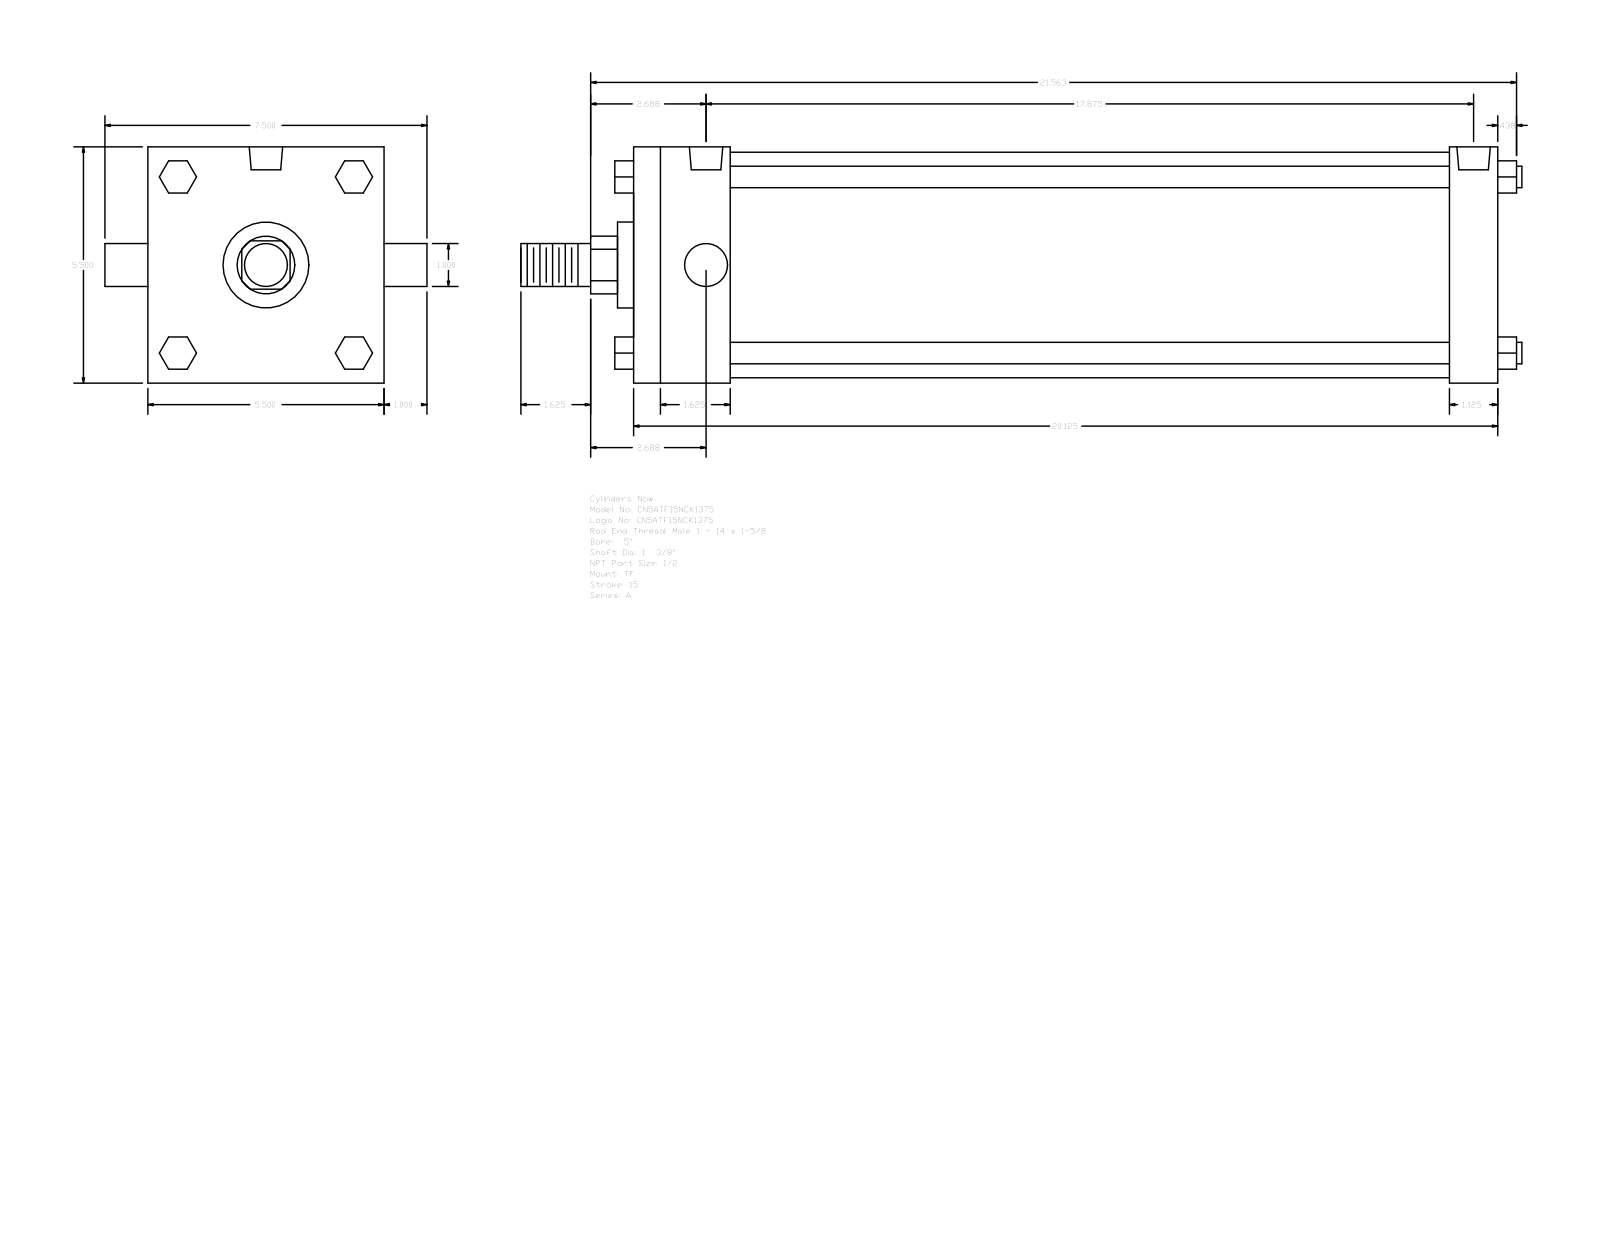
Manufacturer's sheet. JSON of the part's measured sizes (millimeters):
{"part_name": "A_TF__0500_1.375", "step_written_by": "GSSL Pune (CONFIG_CONTROL_DESIGN)", "units": "millimeters", "bodies": {"solids": 0, "faces": 120, "planar": 92, "cylindrical": 28, "other": 0}, "overall_size": [592.14, 190.5, 139.7], "round_holes": [[8.73, 3], [19.77, 2]], "round_bosses_or_shafts": [[12.7, 4], [25.4, 2], [133.35, 1], [50.8, 1], [34.92, 1]], "partial_cylinders_radius": [[17.06, 1]], "face_to_face_distances": [139.7, 511.18, 57.15, 28.58, 482.6, 425.45, 454.03, 19.05, 52.07, 90.18], "hole_center_spacings": [2.39, 451.64, 449.25, 454.03]}
